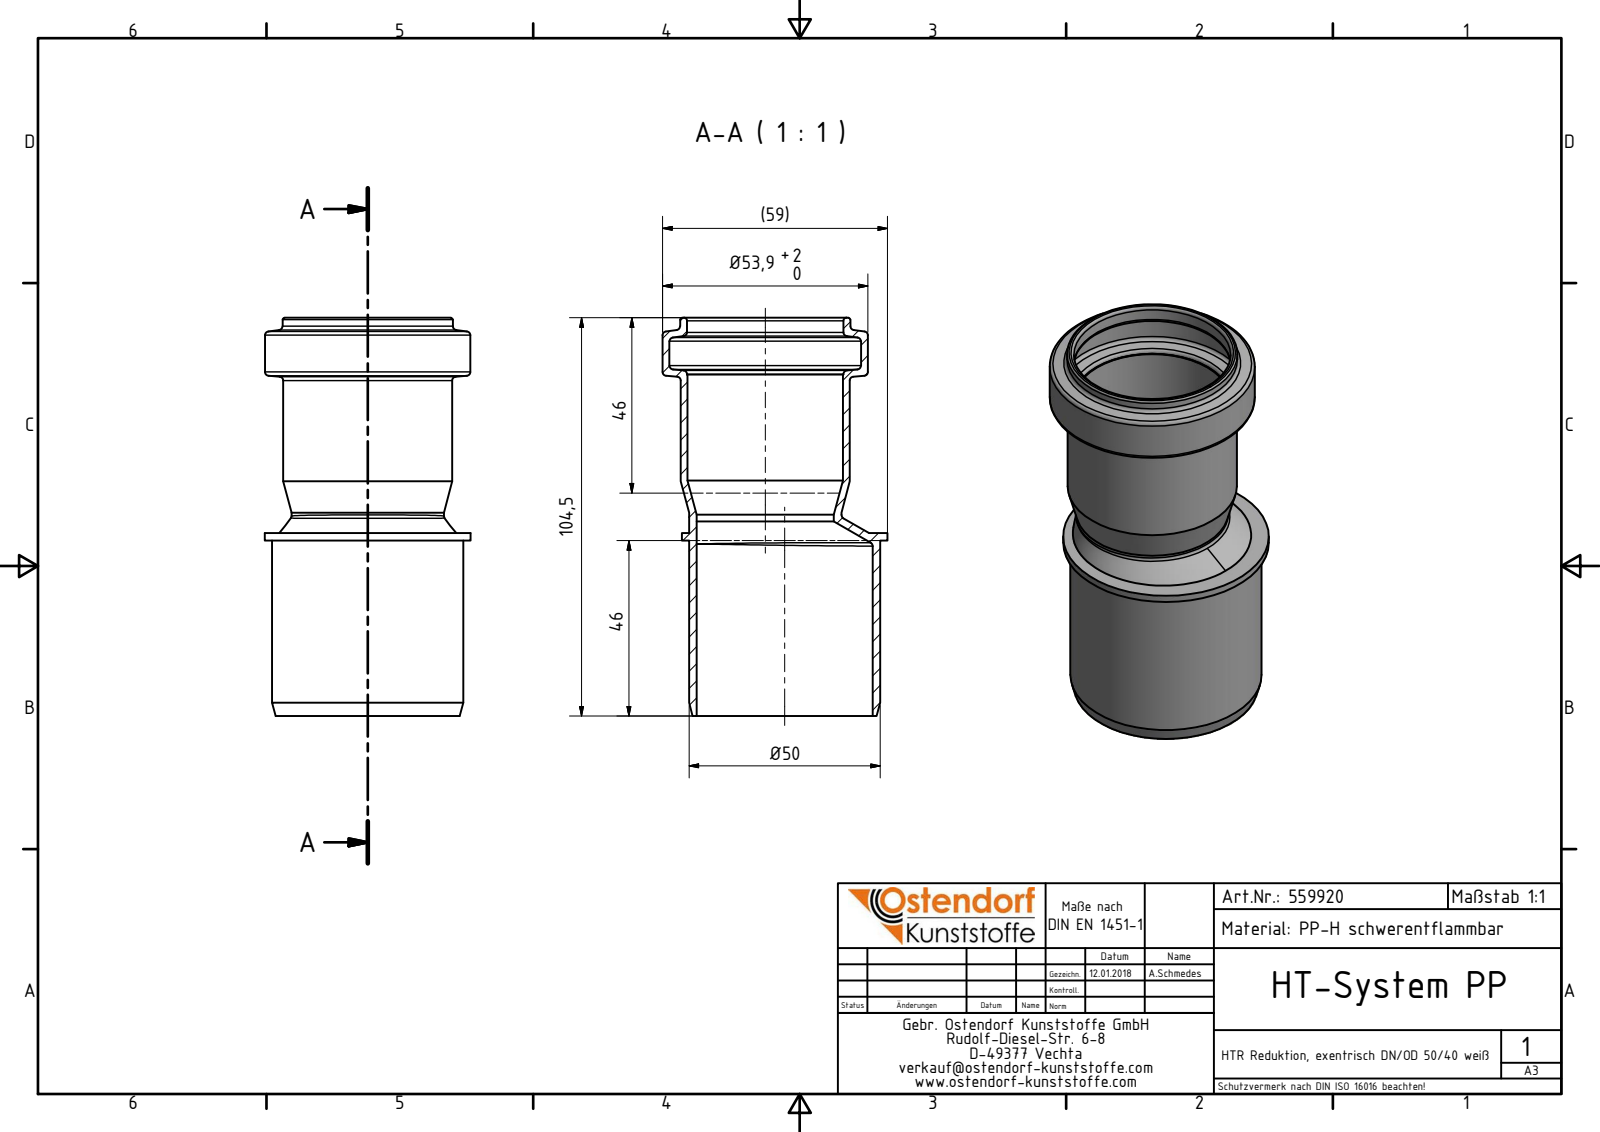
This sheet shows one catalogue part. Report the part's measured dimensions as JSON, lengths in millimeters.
{"part_name": "559920 HTR DN_OD 50_40 weiß", "step_written_by": "Autodesk Inventor 2016 (AUTOMOTIVE_DESIGN)", "units": "millimeters", "bodies": {"solids": 1, "faces": 38, "planar": 5, "cylindrical": 12, "other": 21}, "overall_size": [104.5, 59.05, 54], "volume_mm3": 32199, "surface_area_mm2": 34003, "round_holes": [[36, 1], [40.8, 1], [41.1, 1], [46.2, 1], [50.3, 1]], "round_bosses_or_shafts": [[54, 1], [53.9, 1], [50.2, 1], [44.7, 1], [44.4, 1], [40, 1]], "face_to_face_distances": [2, 46, 48, 104.5, 58.5, 56.5, 89.6, 43.6, 41.6, 14.9], "hole_center_spacings": [5.1]}
